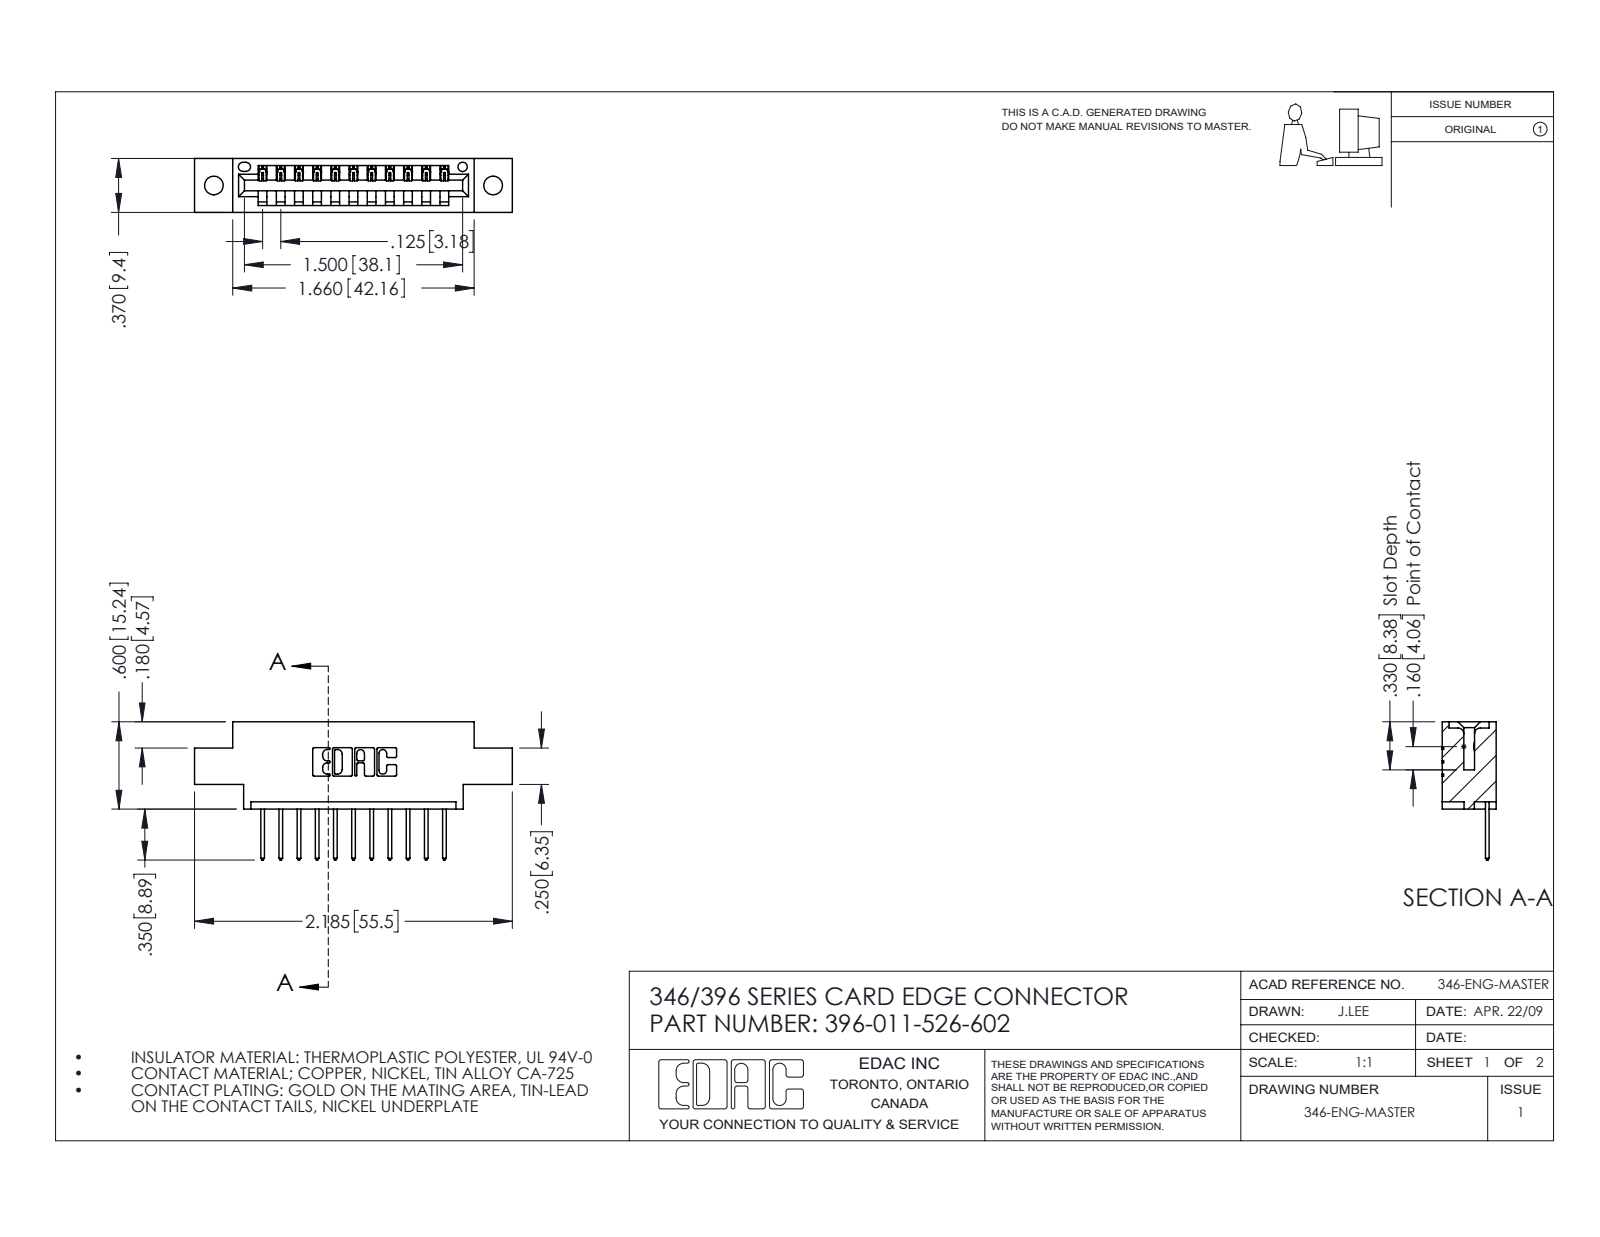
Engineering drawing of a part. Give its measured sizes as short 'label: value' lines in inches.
name: 345-292-001_345-293-126; 346 Part_0.170 Offset - 0.128 Dia; 396-011-526-602
written by: SolidWorks 2016 (CONFIG_CONTROL_DESIGN)
unit: in
bodies: 12 solids, 764 faces (520 planar, 244 cylindrical, 0 other)
size: 2.185 × 0.95 × 0.37
volume: 0.299 in³; area: 8.784 in²
holes: 2× ⌀0.128, 1× ⌀0.064
rounds: 22× R0.006, 22× R0.01, 22× R0.01, 6× R0.007, 6× R0.031, 3× R0.026, 2× R0.031, 2× R0.04
face distances: 0.25, 0.37, 0.048, 0.322, 0.072, 0.298, 0.025, 0.148, 0.222, 0.1
hole spacings: 0.246, 1.715, 1.92
